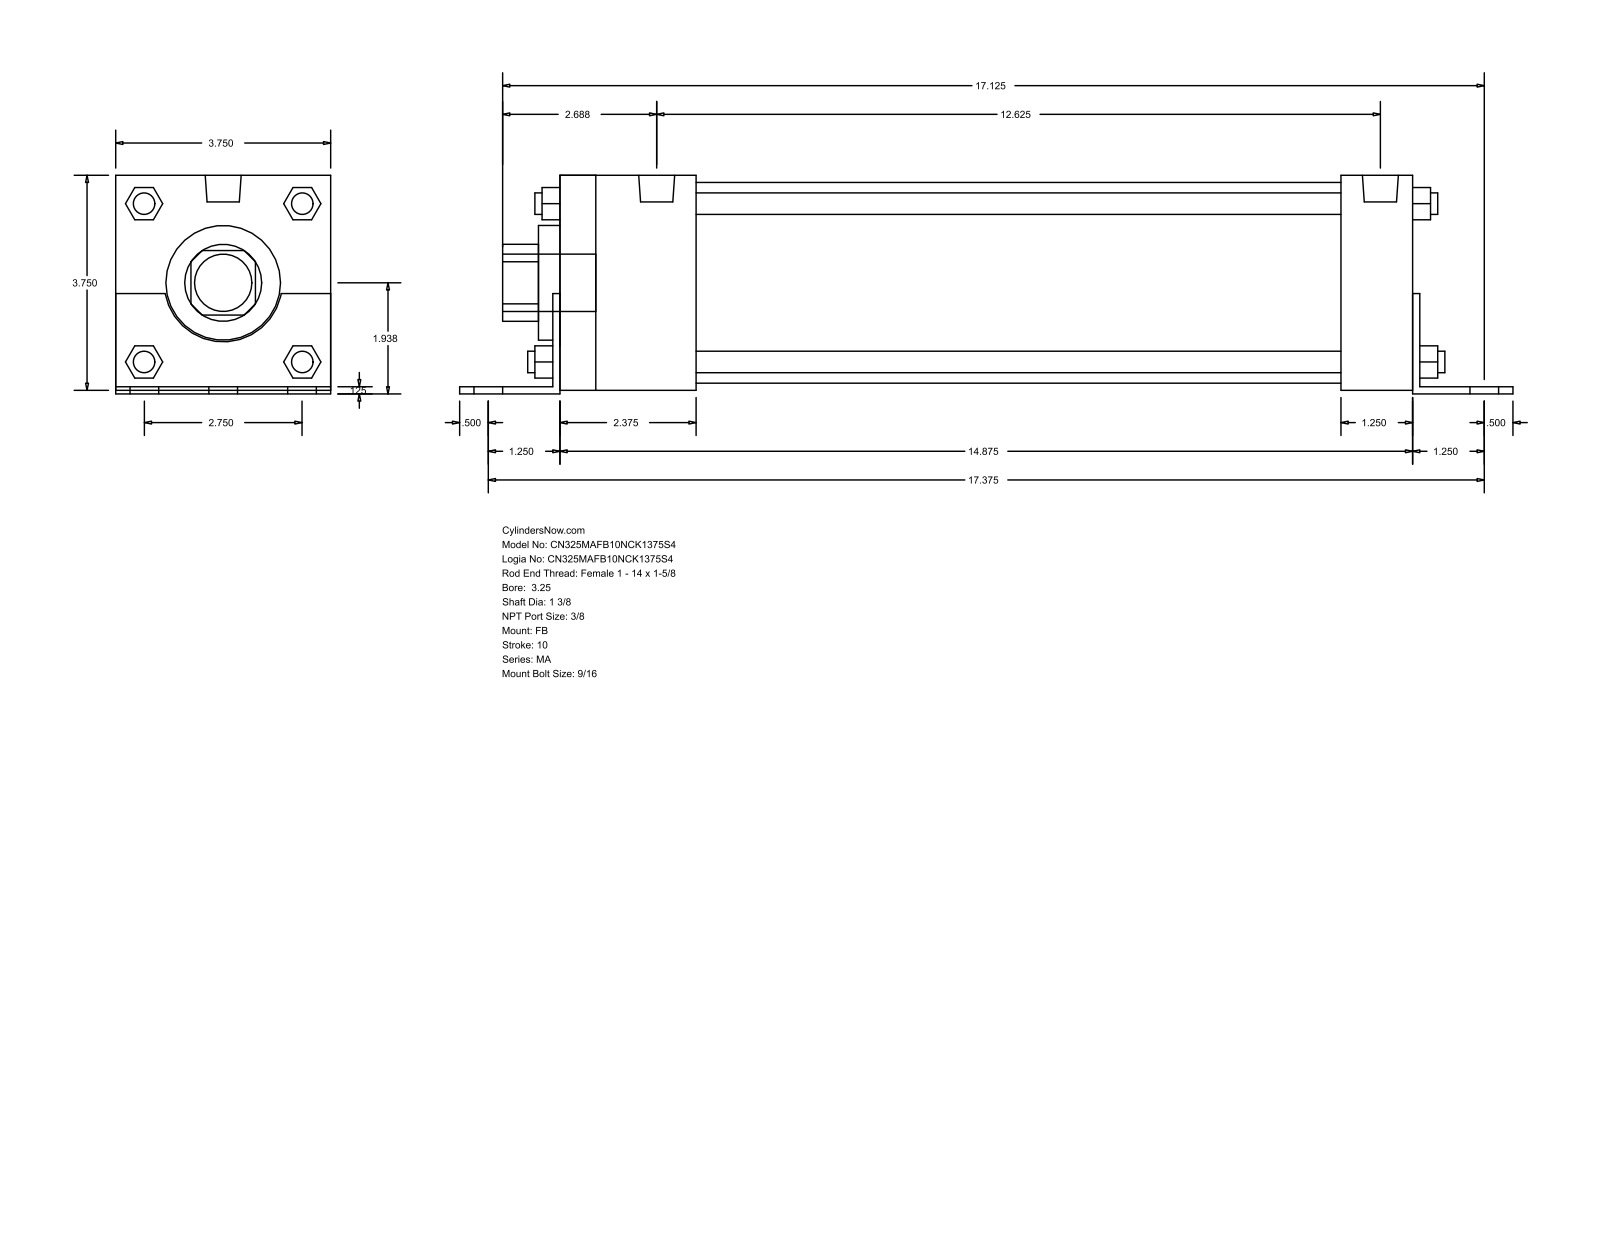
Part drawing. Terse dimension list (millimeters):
name: MA_FB__0325_1.375
written by: GSSL Pune (CONFIG_CONTROL_DESIGN)
unit: mm
bodies: 0 solids, 140 faces (105 planar, 35 cylindrical, 0 other)
size: 466.73 × 96.84 × 95.25
holes: 1× ⌀34.92, 1× ⌀50.8, 1× ⌀88.9
bosses: 6× ⌀14.29, 4× ⌀11.11, 4× ⌀9.53, 2× ⌀15.93, 1× ⌀25.4
rounds: 1× R17.06, 1× R26.16
face distances: 95.24, 3.17, 1.59, 96.83, 1.58, 93.66, 381, 377.83, 31.75, 60.32
